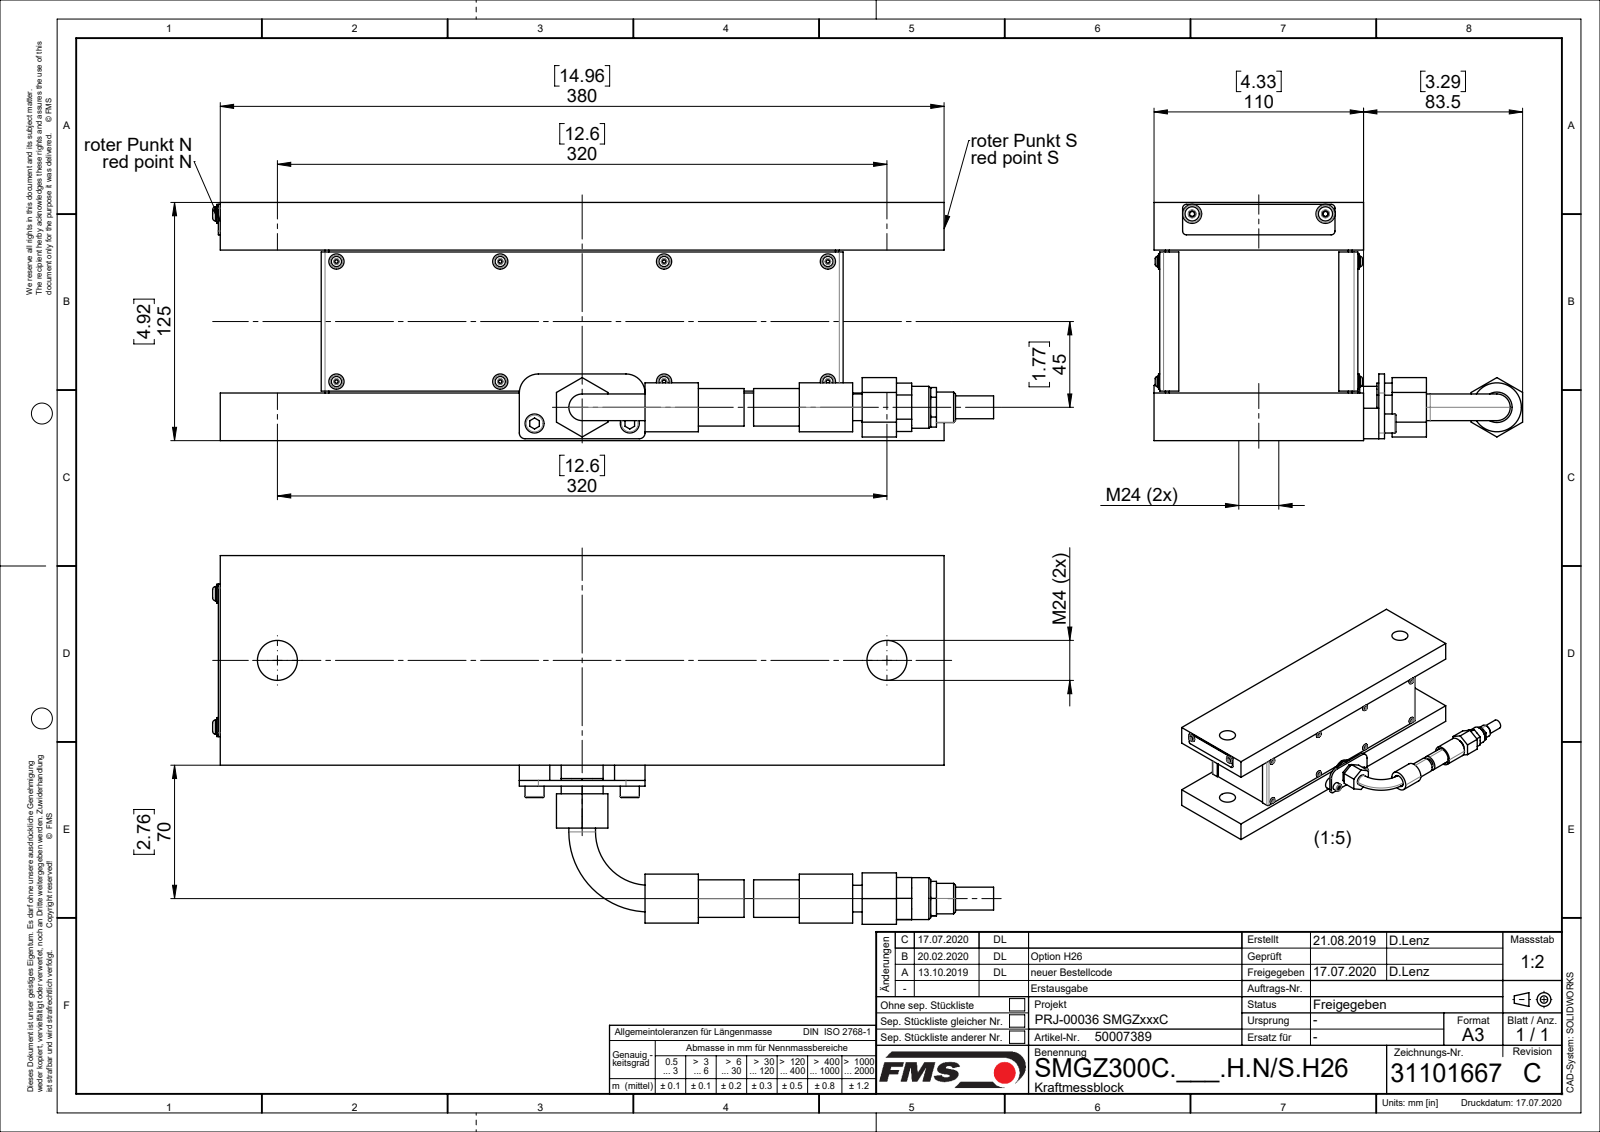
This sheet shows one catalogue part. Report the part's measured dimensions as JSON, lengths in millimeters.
{"part_name": "31101616_01; 31101667_stp; Zyl-Schr DIN912_M6x20; Ls-Schr eco-fix BN10649_M3x8 (+8 more)", "step_written_by": "SolidWorks 2018 (CONFIG_CONTROL_DESIGN)", "units": "millimeters", "bodies": {"solids": 46, "faces": 1359, "planar": 353, "cylindrical": 814, "other": 192}, "overall_size": [410, 193.5, 125], "volume_mm3": 4195000, "surface_area_mm2": 480667, "round_holes": [[2.5, 8], [4, 8], [5.4, 8], [10, 3], [3.3, 2], [4.2, 2], [5, 2], [6.5, 2], [7, 2], [7.5, 2], [9, 2], [12, 2]], "round_bosses_or_shafts": [[8, 8], [3, 8], [10, 4], [22, 2], [19.7, 2], [17, 2], [16, 2], [15.5, 2]], "partial_cylinders_radius": [[0.29, 96], [0.4, 24], [2, 20], [1, 12], [3, 2], [10, 2], [11.5, 1], [12.5, 1]], "face_to_face_distances": [1, 100, 2, 101, 3, 102, 104, 99, 125, 103], "hole_center_spacings": [86, 106.61, 53.3, 63, 132.79, 172, 183.17, 26.41]}
